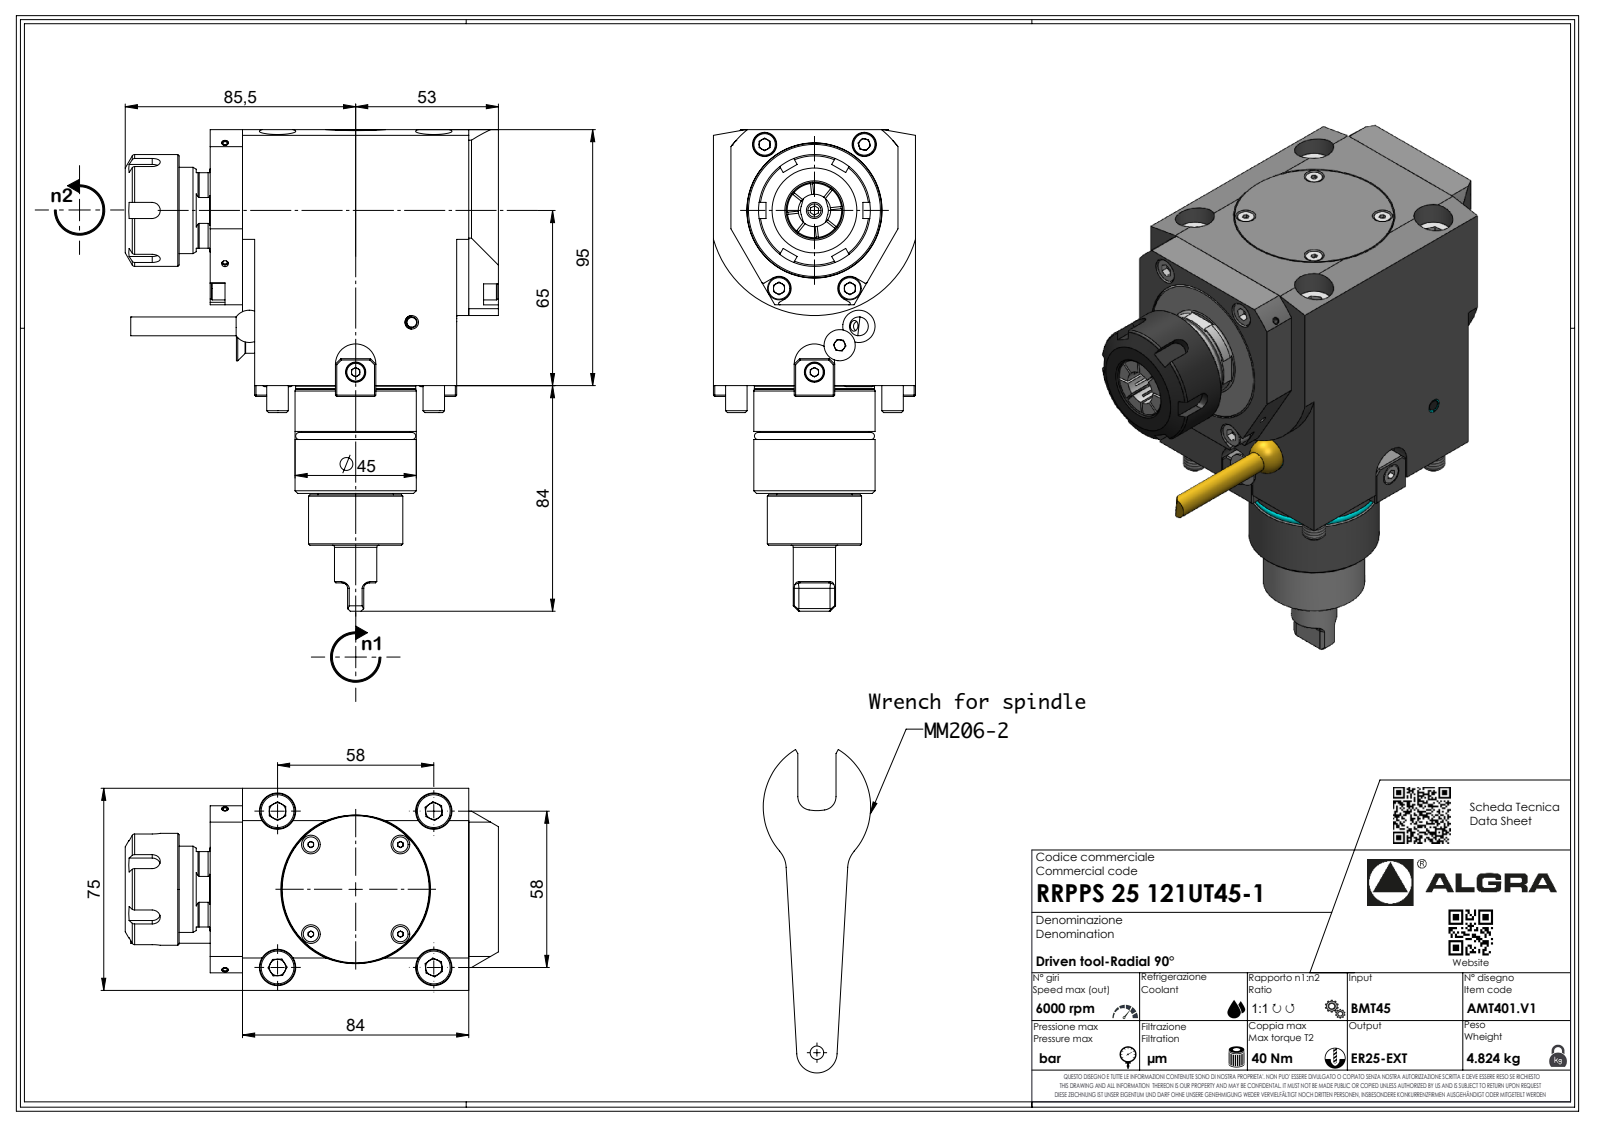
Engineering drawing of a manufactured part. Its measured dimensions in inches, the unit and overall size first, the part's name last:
Units: inches
Overall size (bounding box): 7.035 × 5.454 × 2.953
Round holes (diameter × count): ⌀0.083 ×1, ⌀2.126 ×1
Round bosses / shafts (diameter × count): ⌀0.315 ×4, ⌀1.772 ×1, ⌀1.756 ×1, ⌀1.634 ×1, ⌀1.583 ×1, ⌀1.378 ×1, ⌀1.26 ×1, ⌀1.102 ×1
Partial cylindrical surfaces — rounded edges, fillets, slot ends (radius × count): R0.013 ×7, R0.02 ×7, R0.146 ×7, R0.079 ×6, R0.118 ×5, R0.02 ×4, R0.177 ×4, R0.295 ×2
Main face-to-face distances: 2.953, 3.74, 3.563, 0.61, 3.602, 0.65, 4.213, 0.177, 3.13, 0.433
Volume: 46.51 in³ · Surface area: 99.35 in²
Bodies: 1 solid, 644 faces (440 planar, 86 cylindrical, 118 other)
Part name (STEP PRODUCT): RRPPS25121UT45-1
STEP written by: SolidWorks 2023 (AUTOMOTIVE_DESIGN)
